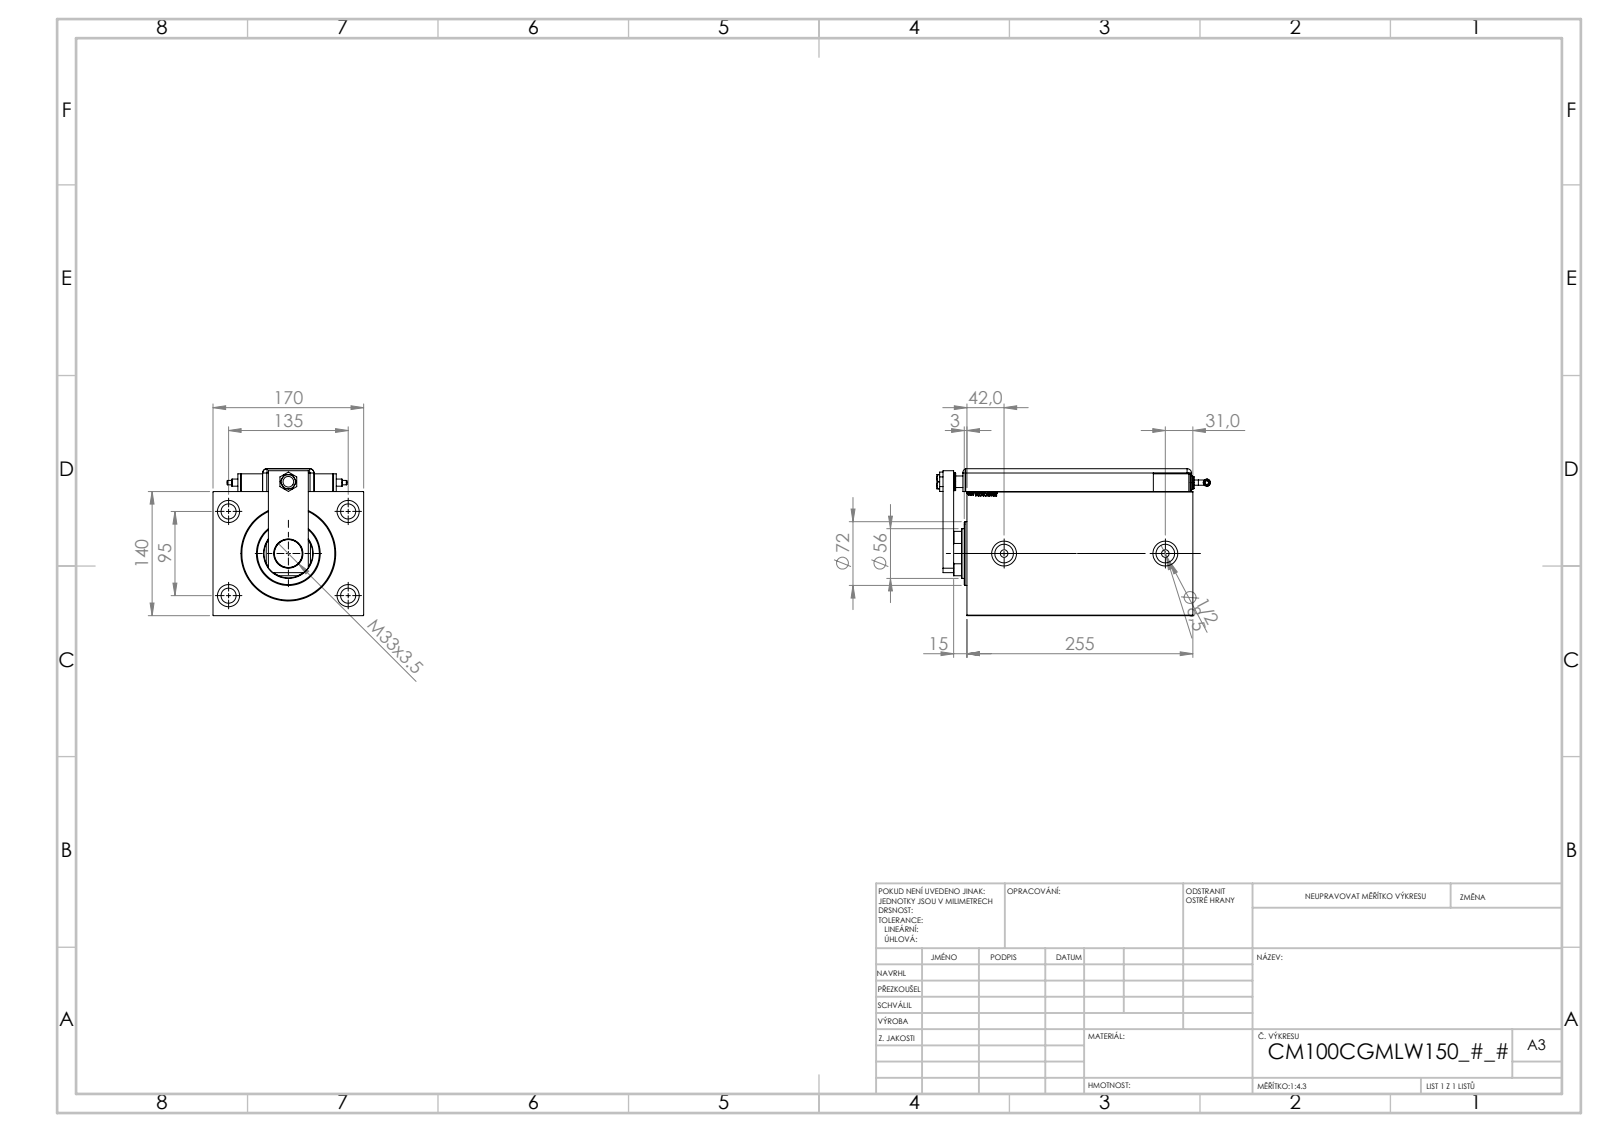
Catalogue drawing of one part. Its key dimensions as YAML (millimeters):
part_name: "ZARAZKA_Q; KRYT; V450CM_C_Body; SWITCH Q (+7 more)"
step_written_by: "SolidWorks 2019 (CONFIG_CONTROL_DESIGN)"
units: millimeters
bodies: {solids: 13, faces: 1277, planar: 619, cylindrical: 125, other: 533}
overall_size: [308.66, 170, 165.8]
volume: 5098000
surface_area: 533062
round_holes:
  - {diameter: 17, count: 4}
  - {diameter: 25, count: 4}
  - {diameter: 4, count: 2}
  - {diameter: 8, count: 2}
  - {diameter: 8.5, count: 2}
  - {diameter: 20.96, count: 2}
  - {diameter: 28, count: 2}
  - {diameter: 12, count: 1}
  - {diameter: 13, count: 1}
  - {diameter: 14, count: 1}
  - {diameter: 31.5, count: 1}
  - {diameter: 33, count: 1}
round_bosses_or_shafts:
  - {diameter: 20, count: 3}
  - {diameter: 16, count: 2}
  - {diameter: 14, count: 2}
  - {diameter: 8, count: 2}
  - {diameter: 6, count: 2}
  - {diameter: 5.04, count: 2}
  - {diameter: 72, count: 1}
partial_cylinders:
  - {radius: 5, count: 9}
  - {radius: 10, count: 1}
  - {radius: 22, count: 1}
face_to_face_distances: [140, 170, 3, 255, 26, 229, 25.8, 165.8, 162.8, 22.8]
hole_center_spacings: [82.54, 75.36, 95, 135, 145.15, 165.08, 20, 81]
